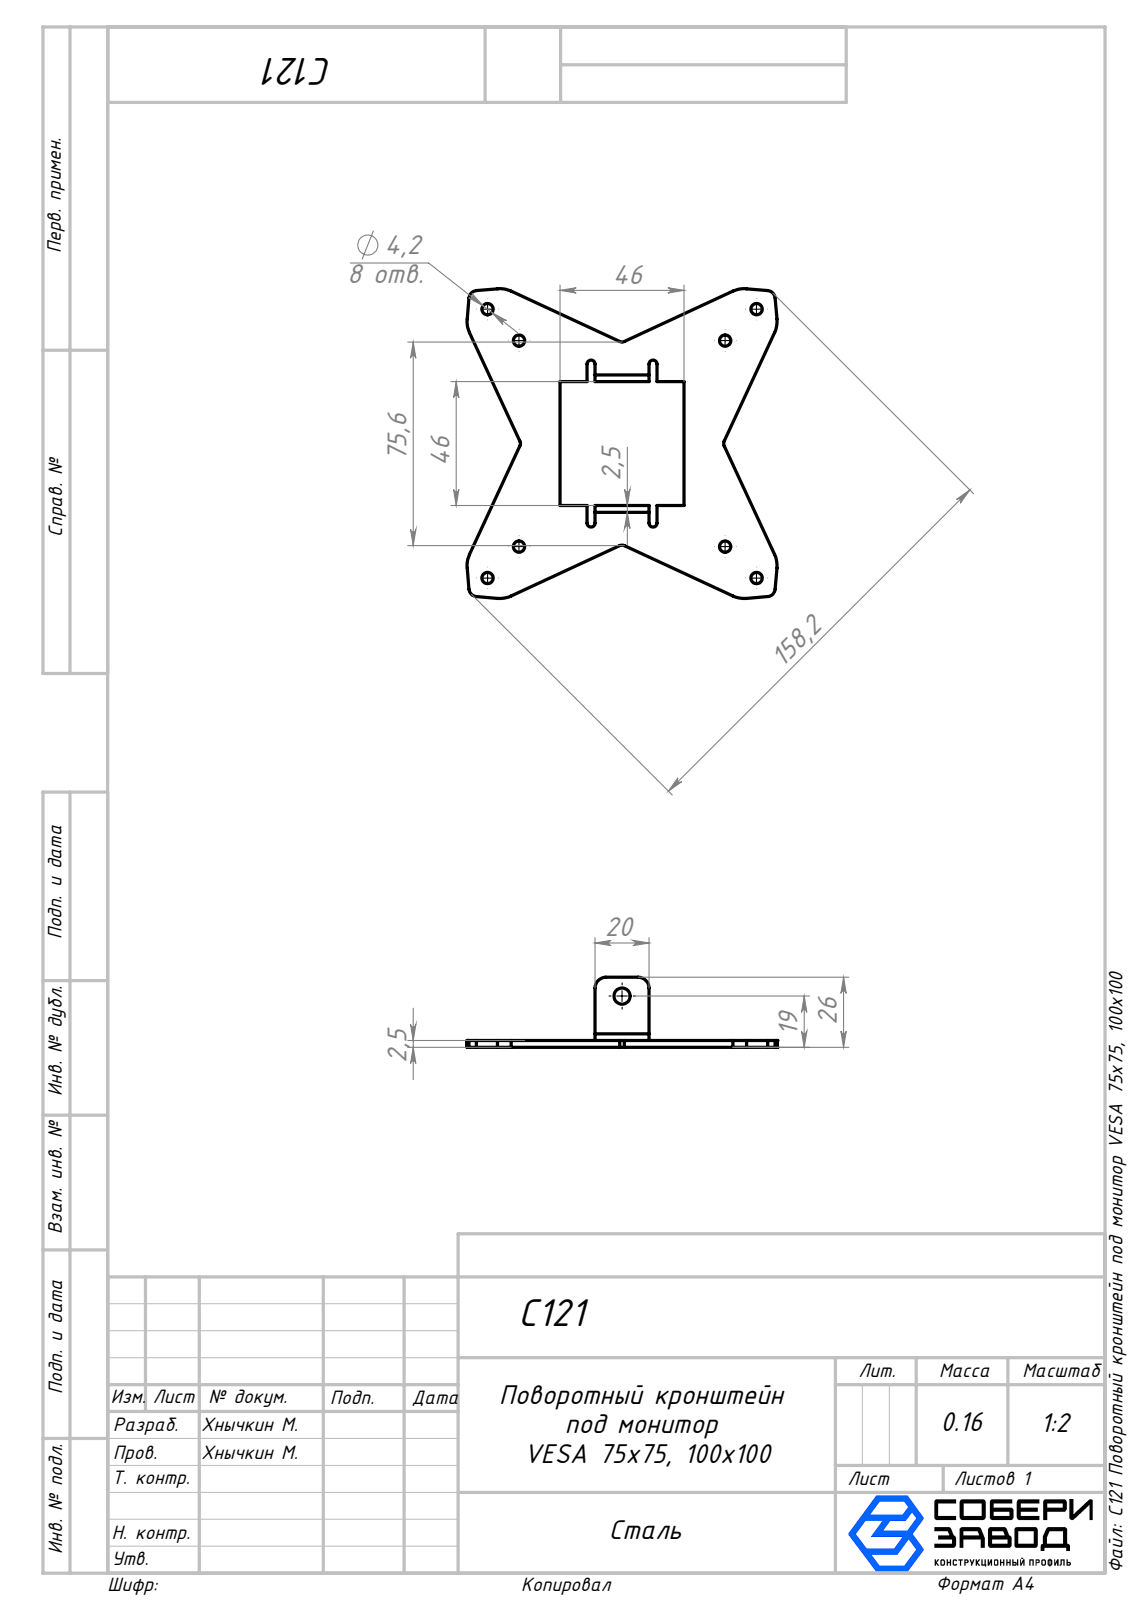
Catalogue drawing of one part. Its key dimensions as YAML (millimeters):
part_name: "C121 Поворотный кронштейн под монитор VESA 75х75, 100х100"
step_written_by: "SolidWorks 2026 (AUTOMOTIVE_DESIGN)"
units: millimeters
bodies: {solids: 1, faces: 91, planar: 38, cylindrical: 53, other: 0}
overall_size: [115, 115, 26]
volume: 20684
surface_area: 18853
round_holes:
  - {diameter: 4.2, count: 8}
  - {diameter: 6, count: 1}
partial_cylinders:
  - {radius: 10, count: 8}
  - {radius: 1.5, count: 4}
  - {radius: 2, count: 4}
  - {radius: 2.5, count: 4}
  - {radius: 3, count: 4}
  - {radius: 4, count: 2}
face_to_face_distances: [2.5, 48.5, 46, 68.02, 51, 13, 33, 20, 26, 122.4]
hole_center_spacings: [88.92, 16.5, 76.48, 99.82, 124.66, 108.16, 141.17]
